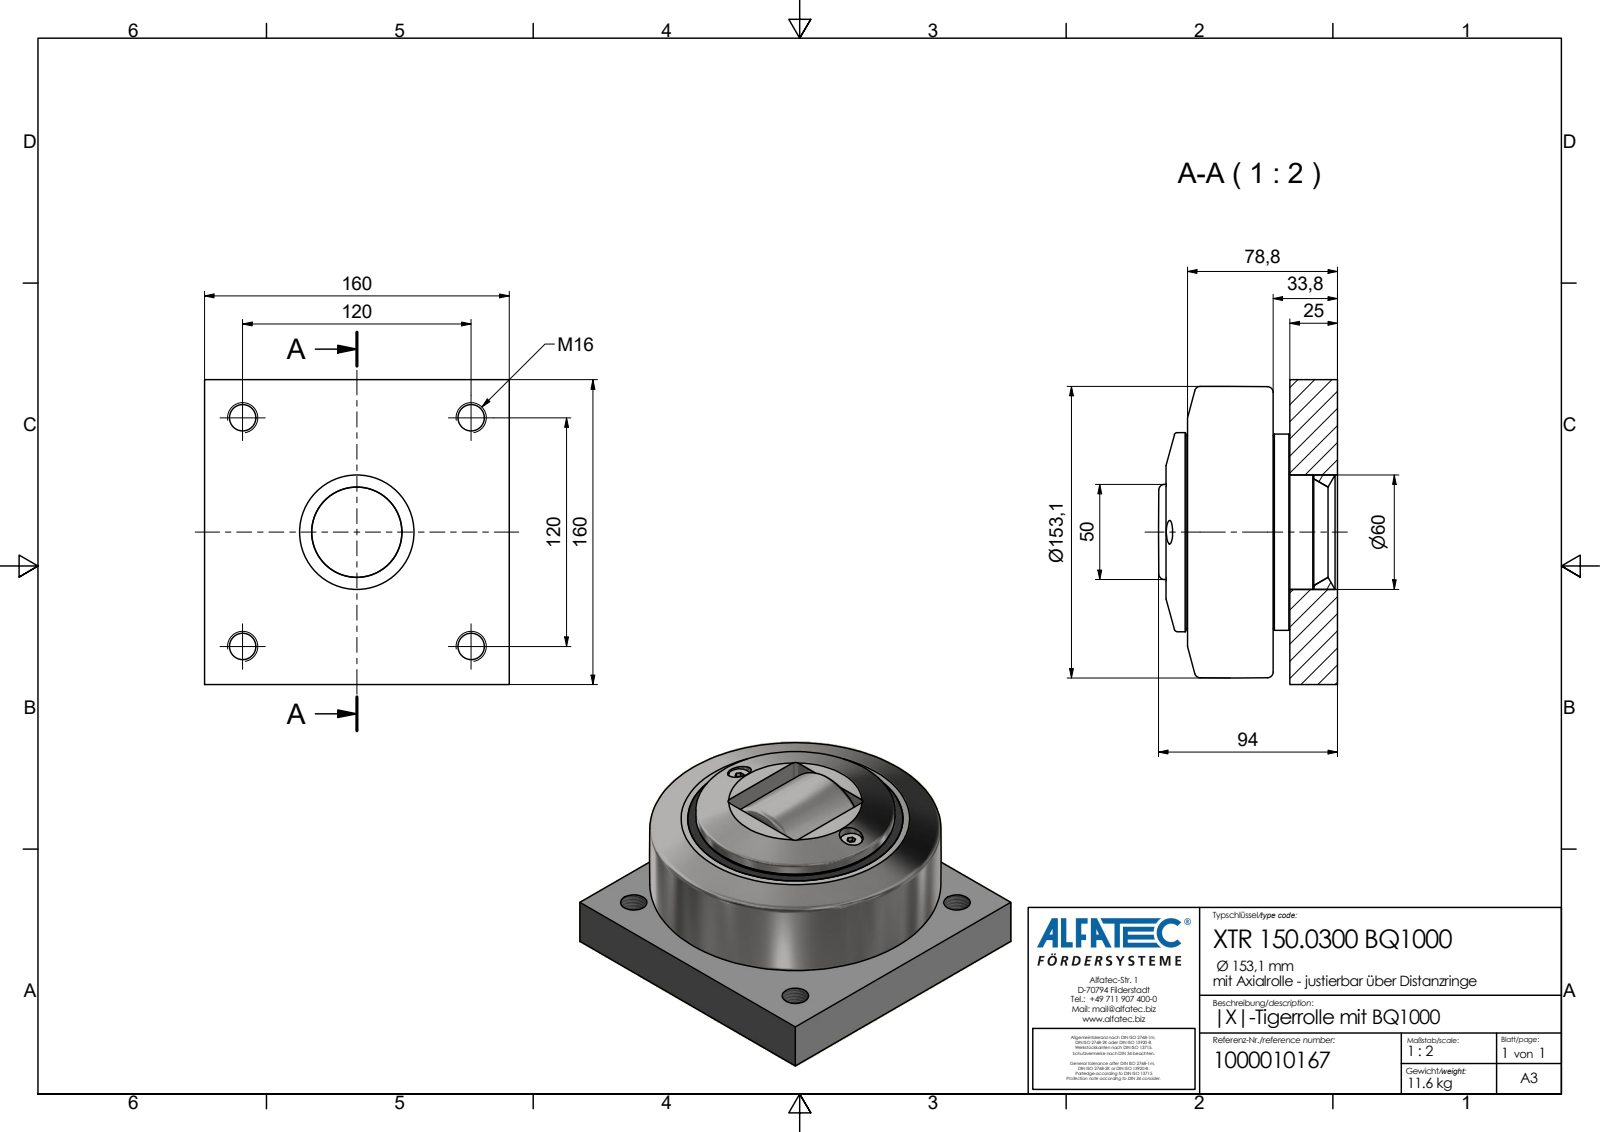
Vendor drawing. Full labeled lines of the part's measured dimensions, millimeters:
Part name (STEP PRODUCT): XTR 150.0300 BQ1000_Kontur
STEP written by: Autodesk Inventor 2020 (AP242_MANAGED_MODEL_BASED_3D_ENGINEERING_MIM_LF)
Units: millimetres
Bodies: 1 solid, 83 faces (47 planar, 22 cylindrical, 14 other)
Overall size (bounding box): 160 × 160 × 94
Volume: 1 588 000 mm³ · Surface area: 119 962 mm²
Round holes (diameter × count): ⌀13.84 ×4, ⌀12.4 ×2
Round bosses / shafts (diameter × count): ⌀11.7 ×2, ⌀104.5 ×1, ⌀103 ×1, ⌀101.4 ×1, ⌀101.2 ×1
Partial cylindrical surfaces — rounded edges, fillets, slot ends (radius × count): R2 ×4, R14.35 ×1, R17.35 ×1, R20.35 ×1
Main face-to-face distances: 25, 33.8, 8.8, 160, 78.8, 53.8, 45, 54.4, 105.6, 90
Hole centre spacings: 62.79, 117.91, 120, 169.71, 83
